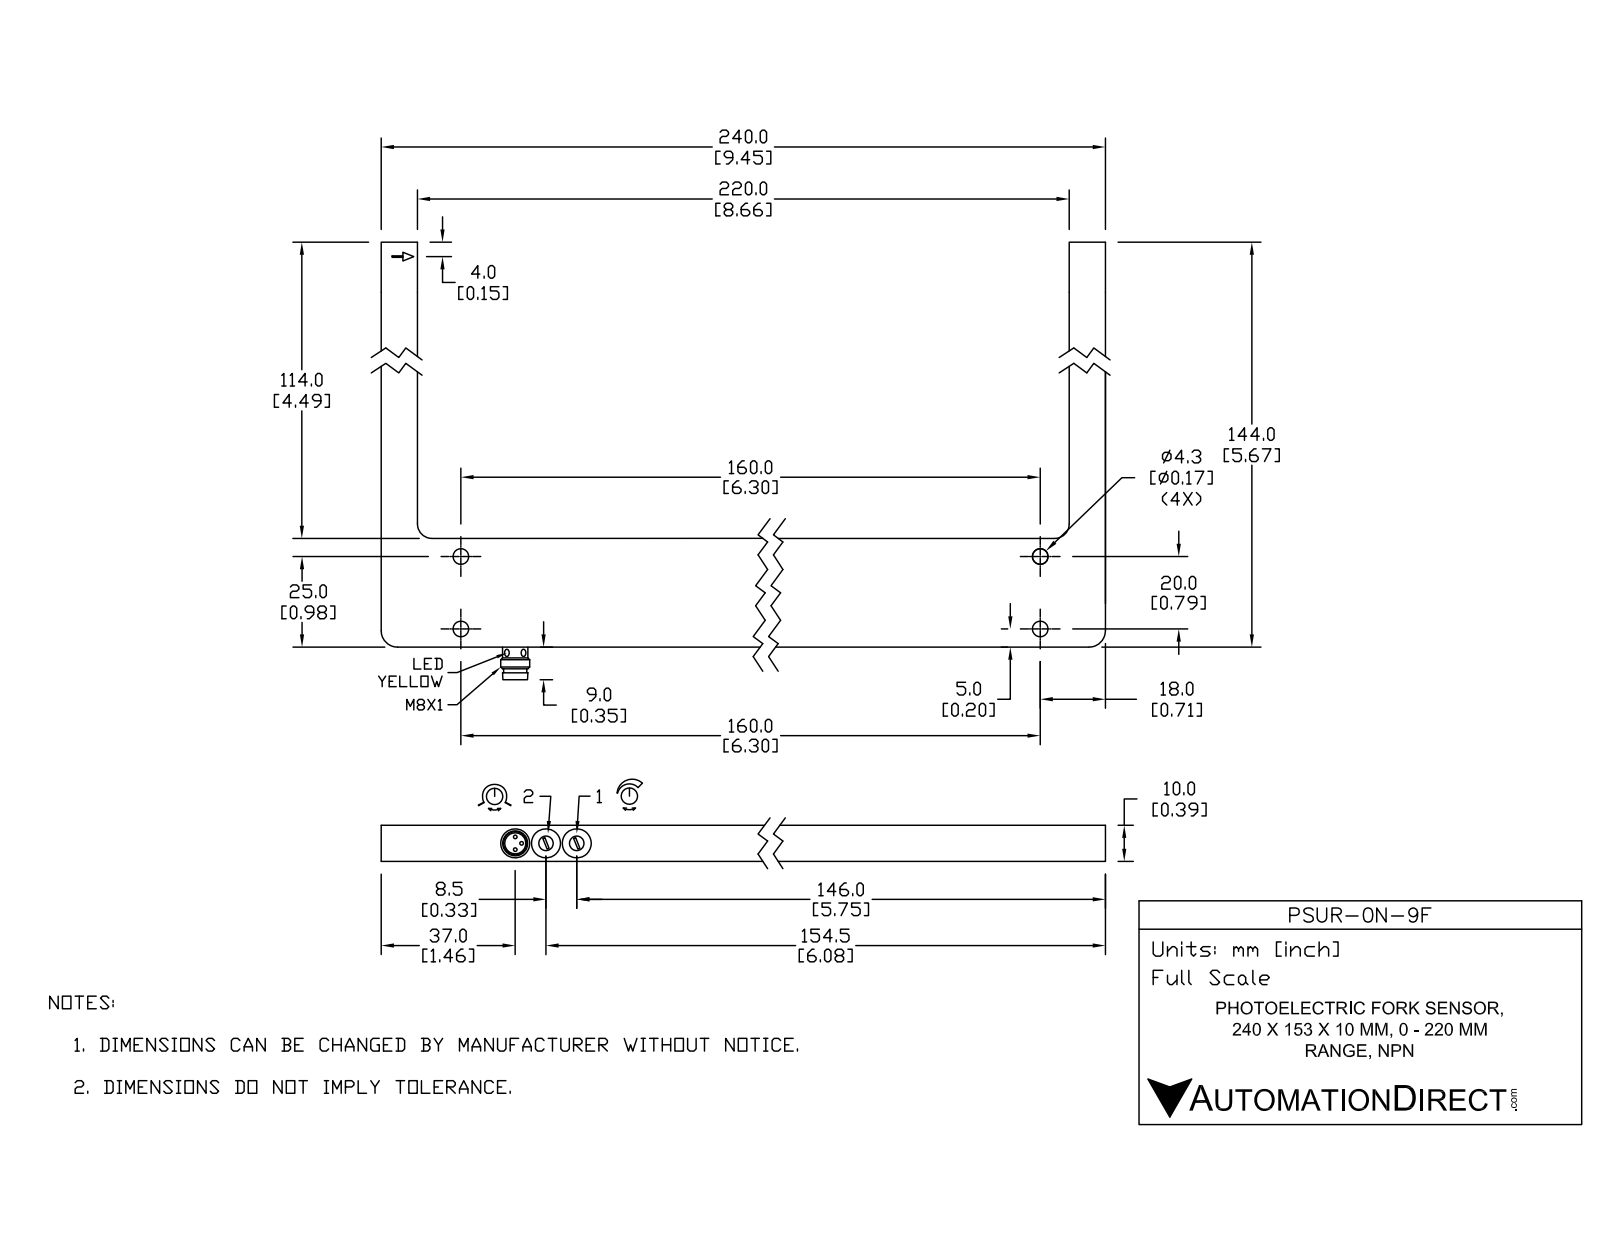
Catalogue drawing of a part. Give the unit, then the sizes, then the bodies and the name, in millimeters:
Units: millimetres
Overall size (bounding box): 240 × 153 × 10
Round holes (diameter × count): ⌀4.3 ×4, ⌀2 ×2, ⌀4 ×2, ⌀8 ×2, ⌀5.8 ×1
Round bosses / shafts (diameter × count): ⌀8 ×1, ⌀6.8 ×1
Partial cylindrical surfaces — rounded edges, fillets, slot ends (radius × count): R1.6 ×2, R4 ×2, R5 ×2
Main face-to-face distances: 10, 230, 30, 240, 220, 114, 144, 143.9, 29.9, 4
Hole centre spacings: 8.5, 20, 200, 201, 17
Volume: 94 390 mm³ · Surface area: 29 590 mm²
Bodies: 1 solid, 81 faces (35 planar, 40 cylindrical, 6 other)
Part name (STEP PRODUCT): PSUR-0N-9F
STEP written by: SolidWorks 2016 (AUTOMOTIVE_DESIGN)
